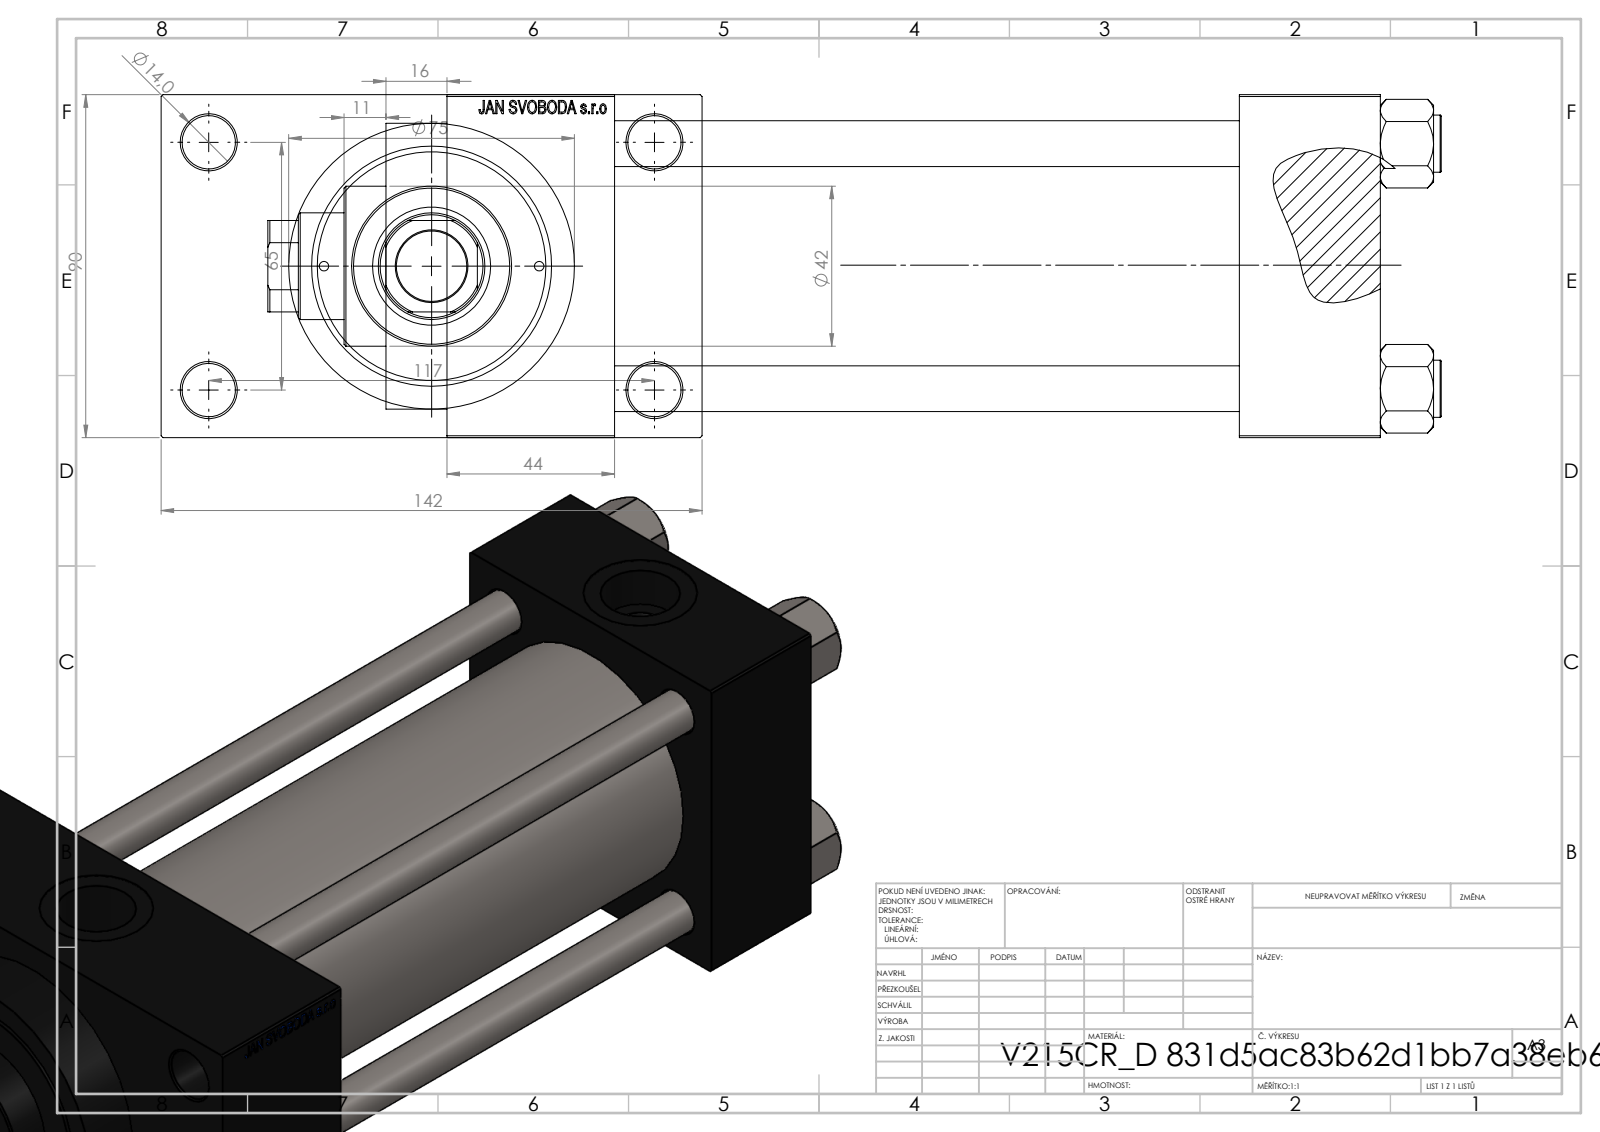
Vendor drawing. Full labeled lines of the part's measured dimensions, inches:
Part name (STEP PRODUCT): NUT_M5_D; V215CR_VCP_D; V215_VC_A; V215CR_D_Body (+1 more)
STEP written by: SolidWorks 2019 (CONFIG_CONTROL_DESIGN)
Units: inches
Bodies: 11 solids, 1112 faces (499 planar, 93 cylindrical, 520 other)
Overall size (bounding box): 12.126 × 5.591 × 3.543
Volume: 78.23 in³ · Surface area: 414.1 in²
Round holes (diameter × count): ⌀0.472 ×4, ⌀0.551 ×4, ⌀0.098 ×2, ⌀0.276 ×2, ⌀0.825 ×2, ⌀1.181 ×2, ⌀0.728 ×1, ⌀1.102 ×1, ⌀1.22 ×1, ⌀1.969 ×1, ⌀2.362 ×1, ⌀2.48 ×1
Round bosses / shafts (diameter × count): ⌀0.591 ×4, ⌀2.953 ×1, ⌀2.717 ×1, ⌀1.654 ×1
Partial cylindrical surfaces — rounded edges, fillets, slot ends (radius × count): R0.531 ×1
Main face-to-face distances: 3.543, 6.457, 1.457, 7.913, 8.189, 9.646, 1.732, 1.024, 4.567, 5.591
Hole centre spacings: 1.037, 1.275, 1.748, 1.79, 2.531, 2.635, 2.694, 2.748
